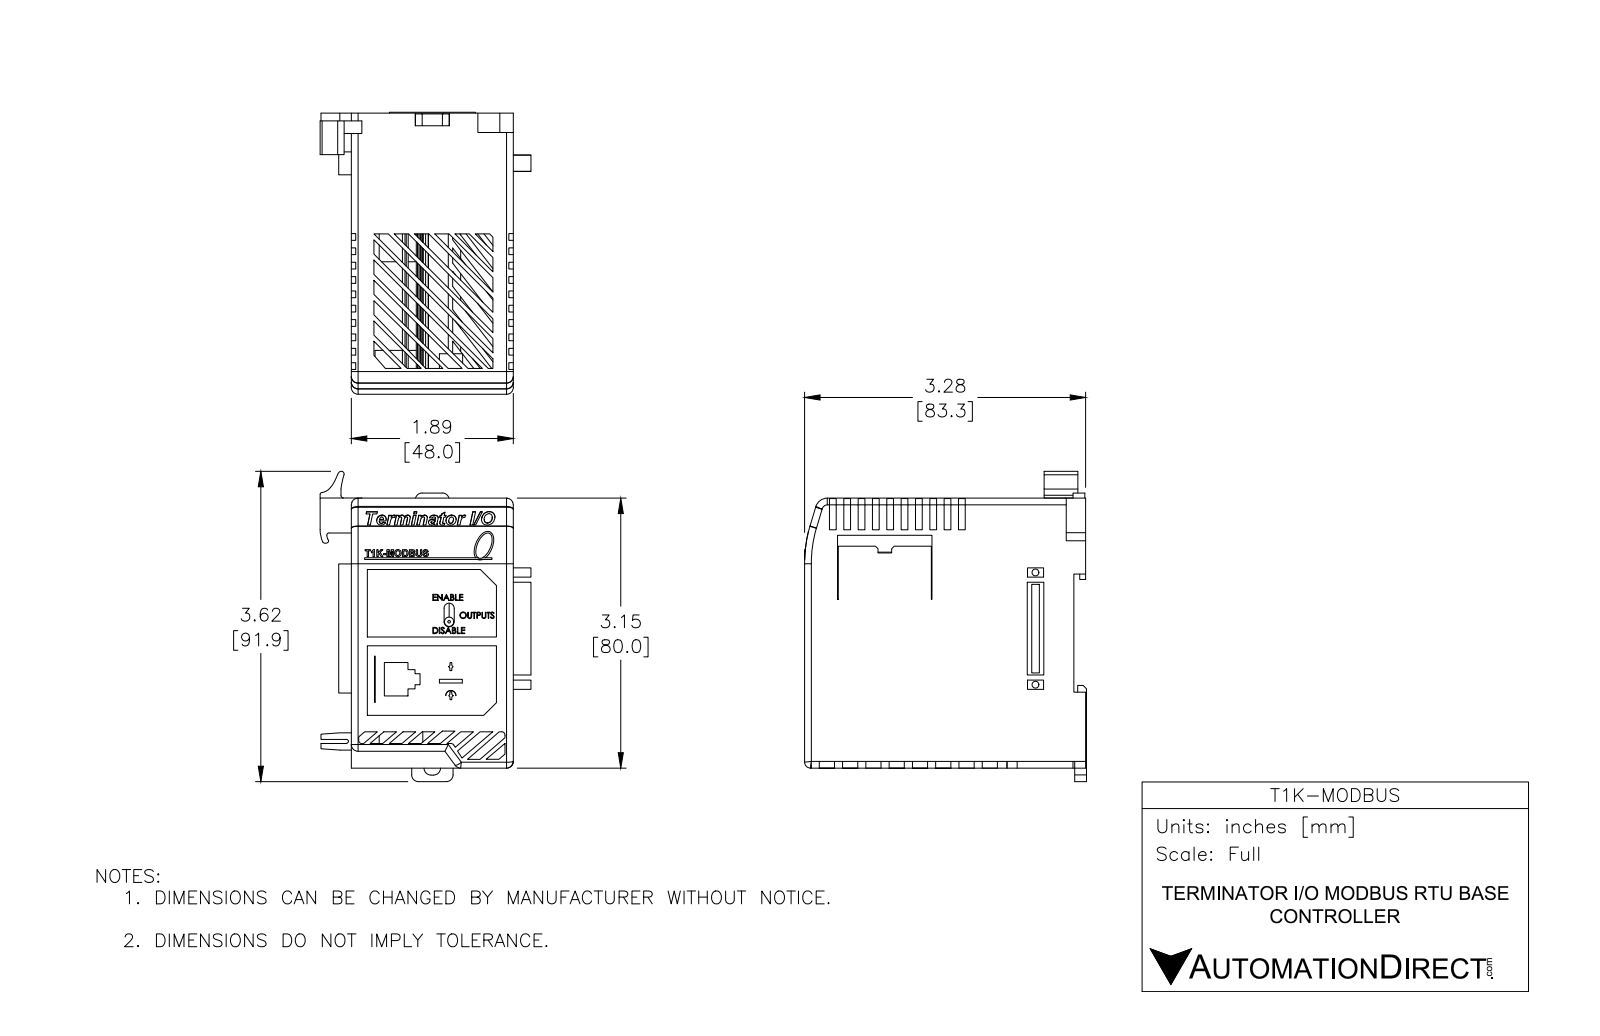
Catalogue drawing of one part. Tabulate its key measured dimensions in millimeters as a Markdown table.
| quantity | value |
| --- | --- |
| part name | T1K-MODBUS |
| STEP written by | SolidWorks 2013 (AUTOMOTIVE_DESIGN) |
| units | millimeters |
| bodies | 25 solids, 1297 faces (939 planar, 74 cylindrical, 284 other) |
| overall size | 91.94 × 83.59 × 62.5 |
| volume | 106 786 mm³ |
| surface area | 61 382 mm² |
| round holes (diameter × count) | 2 × 2, 3.01 × 2 |
| round bosses / shafts (diameter × count) | 1.5 × 2, 3.01 × 1 |
| partial cylindrical surfaces (radius × count) | 2 × 18, 1 × 12, 0.75 × 4, 1.5 × 2, 2.06 × 2, 0.83 × 1, 0.94 × 1, 2.02 × 1 |
| main face-to-face distances | 2, 46, 48, 44, 1, 61, 3.5, 16.8, 77.8, 78 |
| hole center spacings | 8.58, 33.25 |
